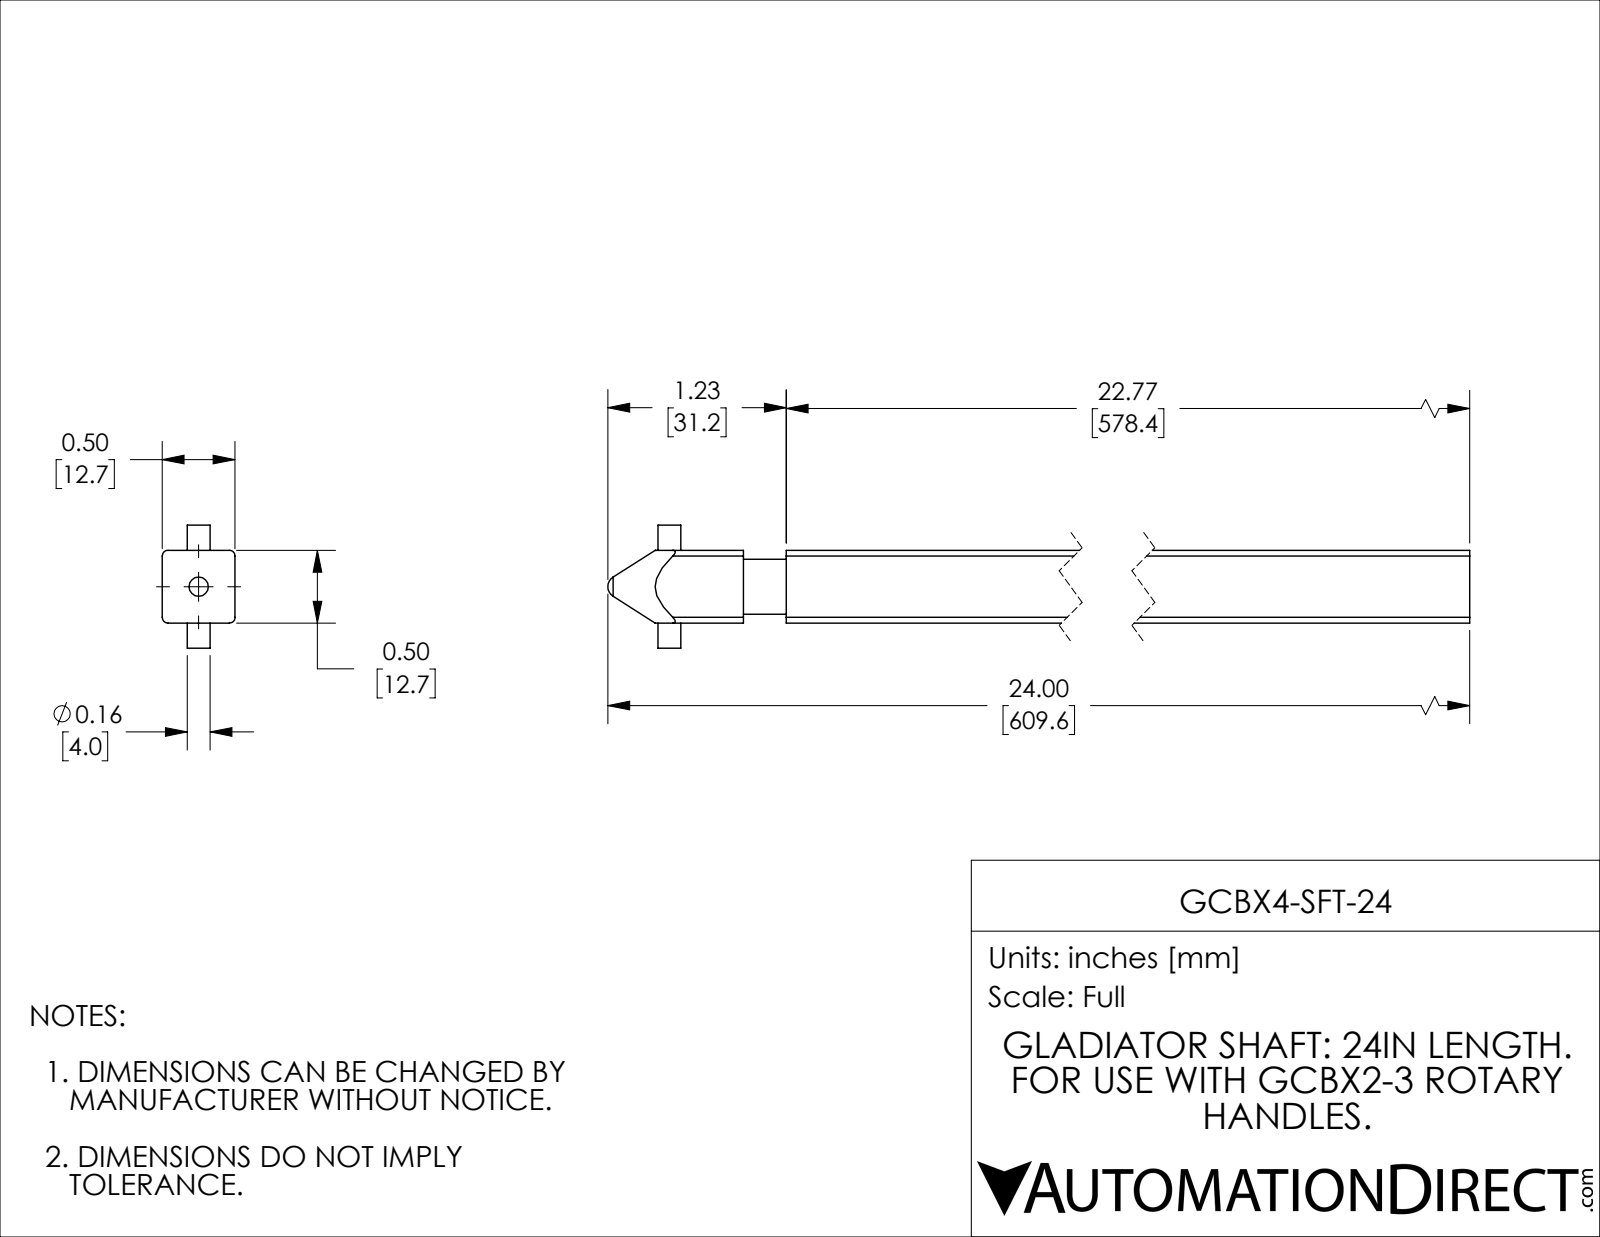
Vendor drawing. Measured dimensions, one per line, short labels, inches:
name: GCBX4-SFT-24
written by: SolidWorks 2021 (CONFIG_CONTROL_DESIGN)
unit: in
bodies: 1 solid, 39 faces (15 planar, 17 cylindrical, 7 other)
size: 23.999 × 0.846 × 0.5
volume: 5.863 in³; area: 46.95 in²
holes: 1× ⌀0.142
bosses: 1× ⌀0.378, 1× ⌀0.157
rounds: 4× R0.039
face distances: 0.5, 22.773, 23.068, 0.295, 0.244, 0.256, 0.173, 0.673, 0.846
